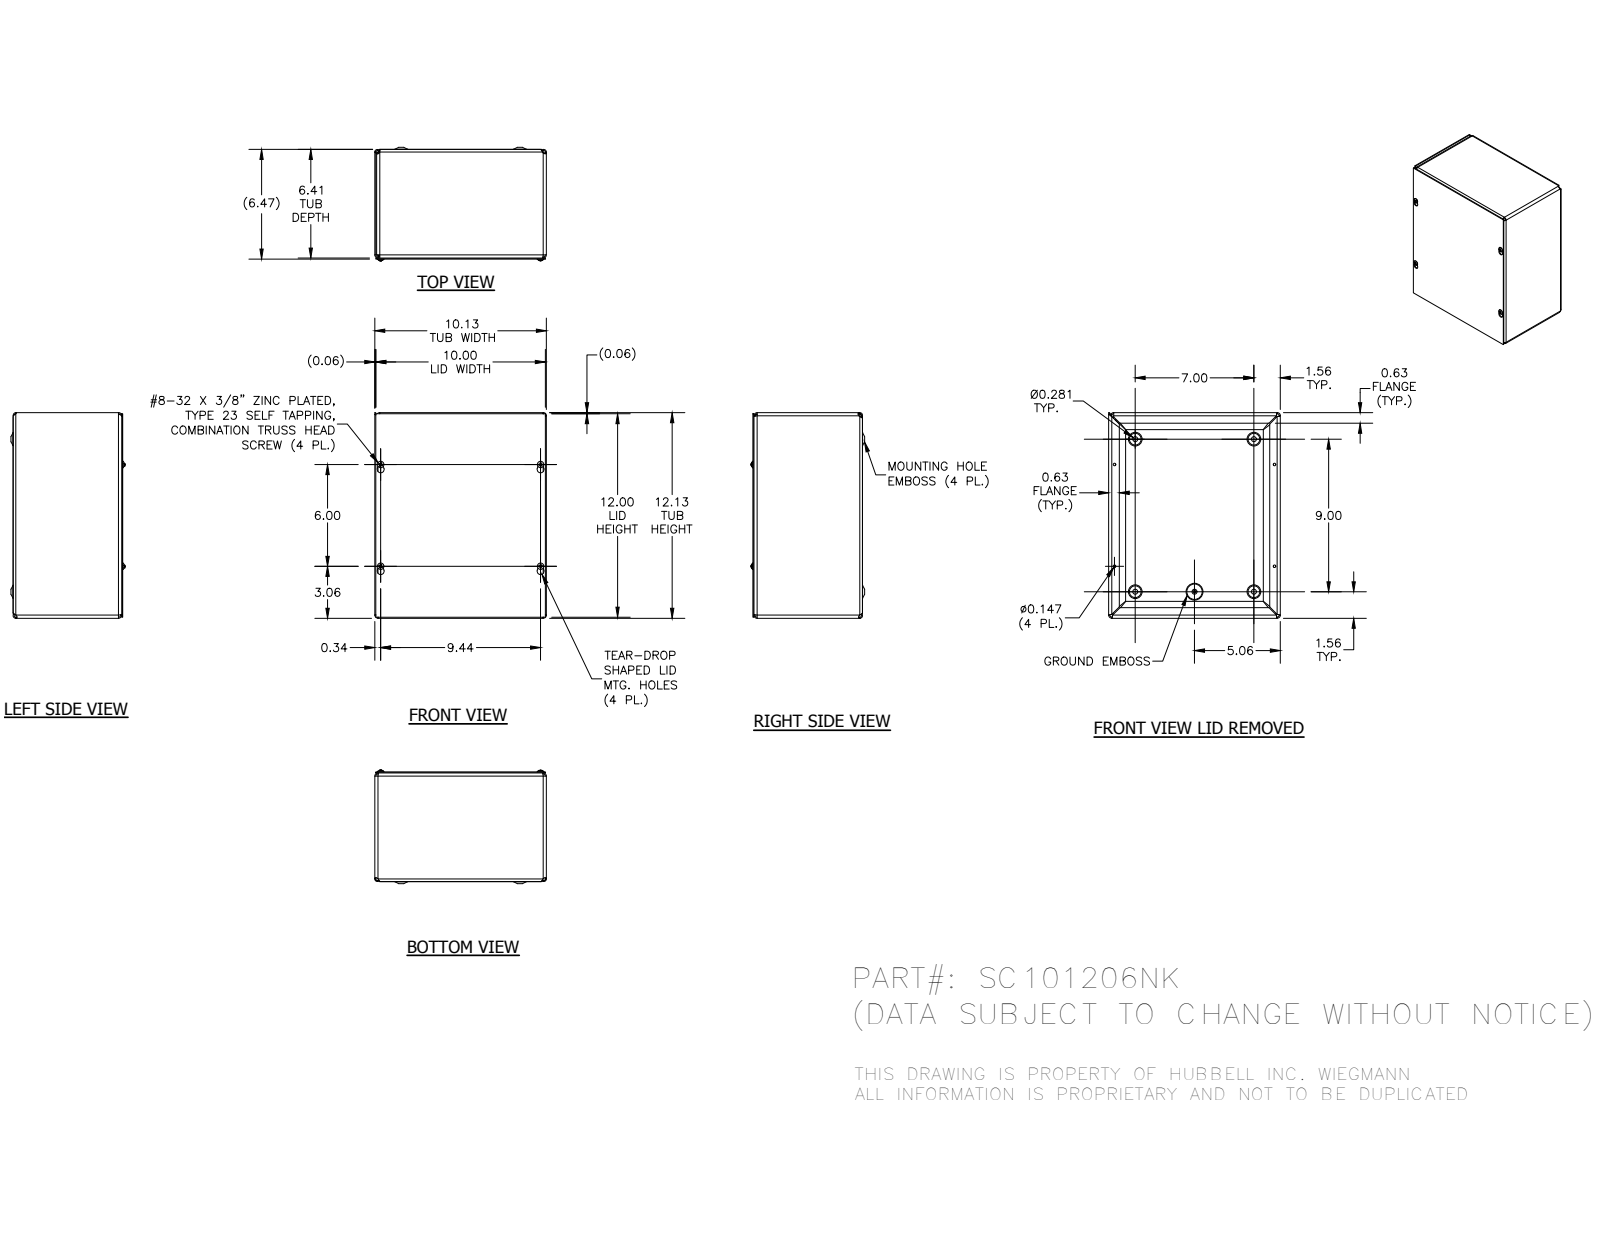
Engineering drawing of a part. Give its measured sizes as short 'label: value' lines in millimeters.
name: SC1012BKP; SC101206NKWRA; SC1012LID; 34056 (+1 more)
written by: Autodesk Inventor 2014 (AUTOMOTIVE_DESIGN)
unit: mm
bodies: 7 solids, 357 faces (132 planar, 67 cylindrical, 158 other)
size: 307.98 × 257.18 × 170
volume: 582 917 mm³; area: 747 975 mm²
holes: 4× ⌀3.73, 4× ⌀7.62, 1× ⌀4.19
bosses: 4× ⌀9.75, 4× ⌀4.17, 1× ⌀5.8
rounds: 12× R3.17, 8× R4.75, 4× R1.4, 4× R1.57, 4× R2.38, 4× R2.97, 4× R3.15, 4× R3.96
face distances: 1.57, 161.12, 1.58, 162.69, 1.59, 162.71, 164.28, 255.6, 254.03, 257.18
hole spacings: 49.09, 193, 282.61, 88.9, 152.4, 177.8, 212.2, 212.21
